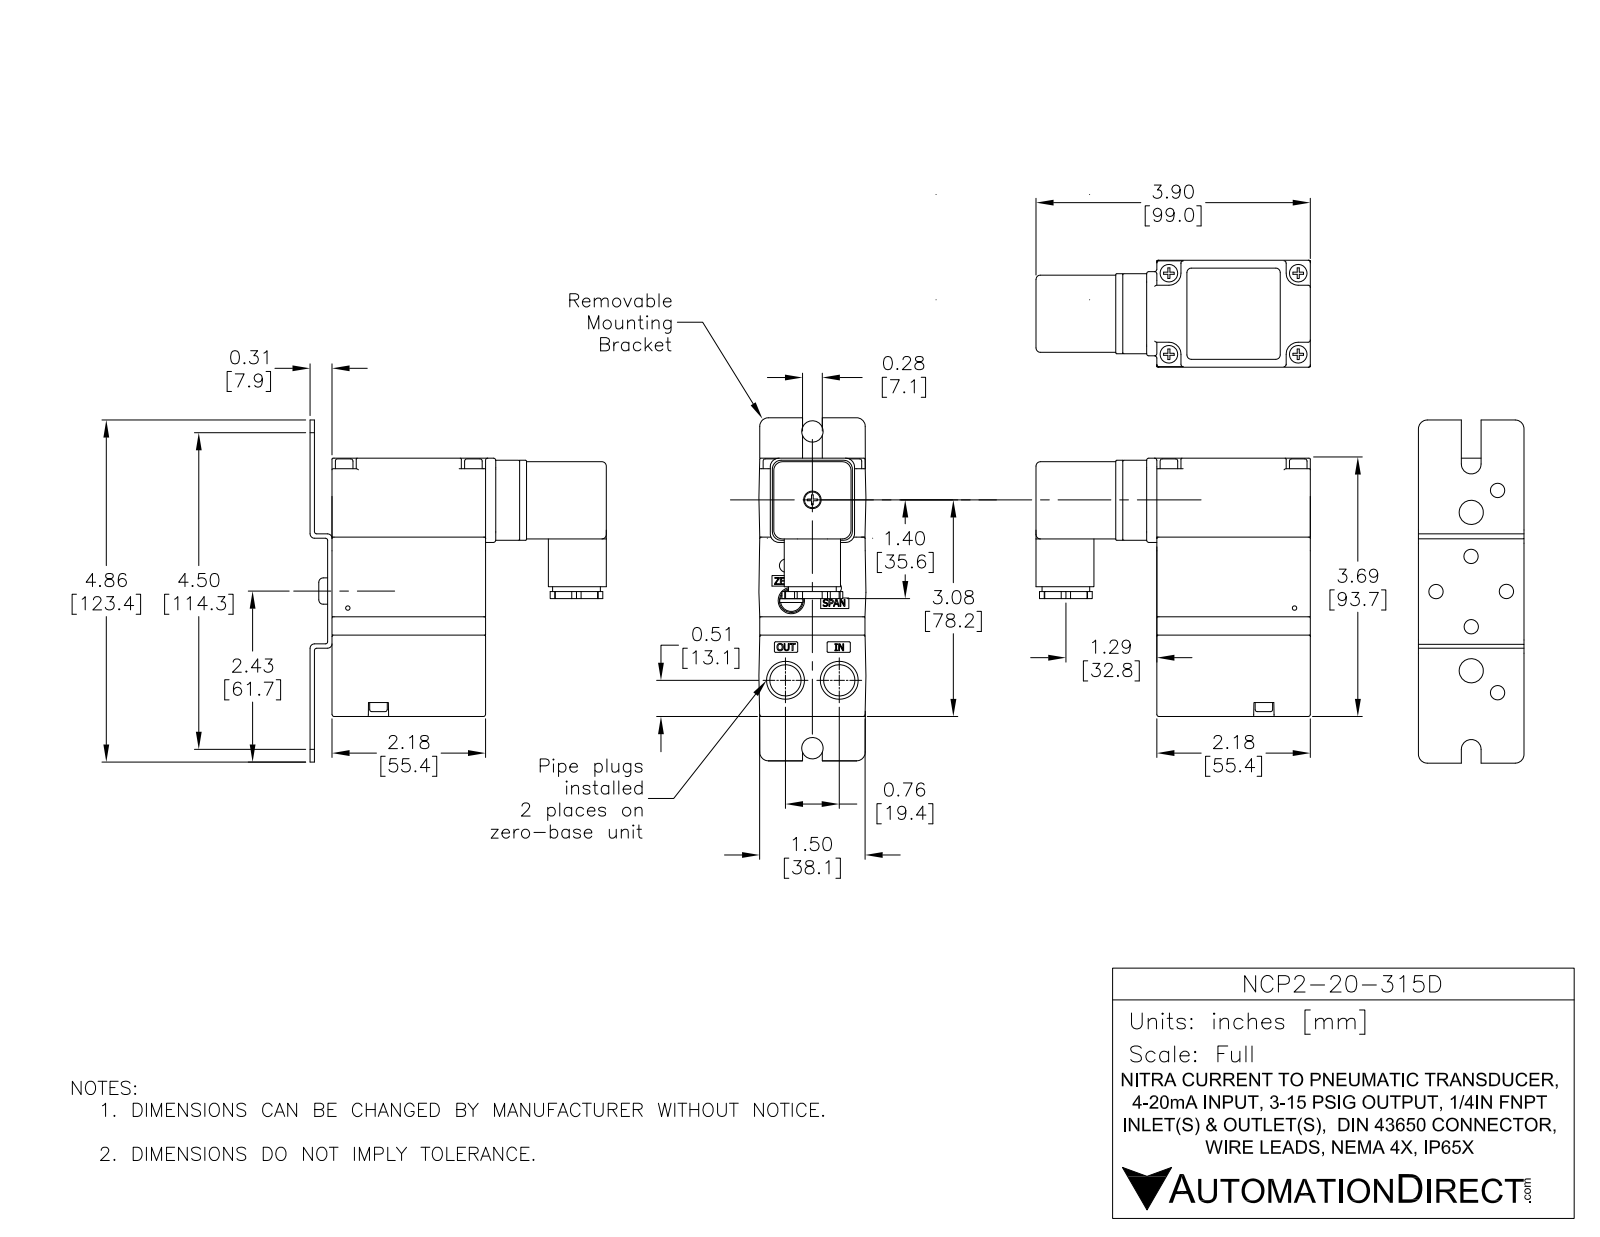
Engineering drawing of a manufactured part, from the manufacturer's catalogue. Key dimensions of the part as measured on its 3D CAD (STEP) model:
Part name (STEP PRODUCT): NCP2-20-315D
STEP written by: SolidWorks 2016 (AUTOMOTIVE_DESIGN)
Units: millimetres
Bodies: 5 solids, 1129 faces (622 planar, 321 cylindrical, 186 other)
Overall size (bounding box): 123.83 × 107.43 × 38.77
Volume: 223 787 mm³ · Surface area: 53 073 mm²
Round holes (diameter × count): ⌀5.16 ×6, ⌀3.37 ×3, ⌀3.18 ×2, ⌀3.3 ×2, ⌀4.8 ×2, ⌀8.73 ×2, ⌀11.38 ×2, ⌀1.59 ×1, ⌀3.17 ×1, ⌀6.35 ×1, ⌀7.37 ×1, ⌀11.43 ×1
Round bosses / shafts (diameter × count): ⌀6.6 ×4, ⌀6.35 ×3, ⌀7.49 ×2, ⌀20.32 ×1, ⌀18.32 ×1, ⌀16.18 ×1, ⌀11.43 ×1, ⌀8.66 ×1
Partial cylindrical surfaces — rounded edges, fillets, slot ends (radius × count): R0.76 ×56, R3.17 ×20, R0.5 ×17, R0.4 ×12, R1.47 ×6, R1.59 ×6, R0.79 ×4, R1.25 ×4
Main face-to-face distances: 1.59, 6.85, 8.44, 55.55, 37.35, 38.74, 1.39, 6.74, 8.33, 1.69
Hole centre spacings: 25.4, 33.68, 12.4, 17.74, 17.94, 18.41, 18.78, 21.29
